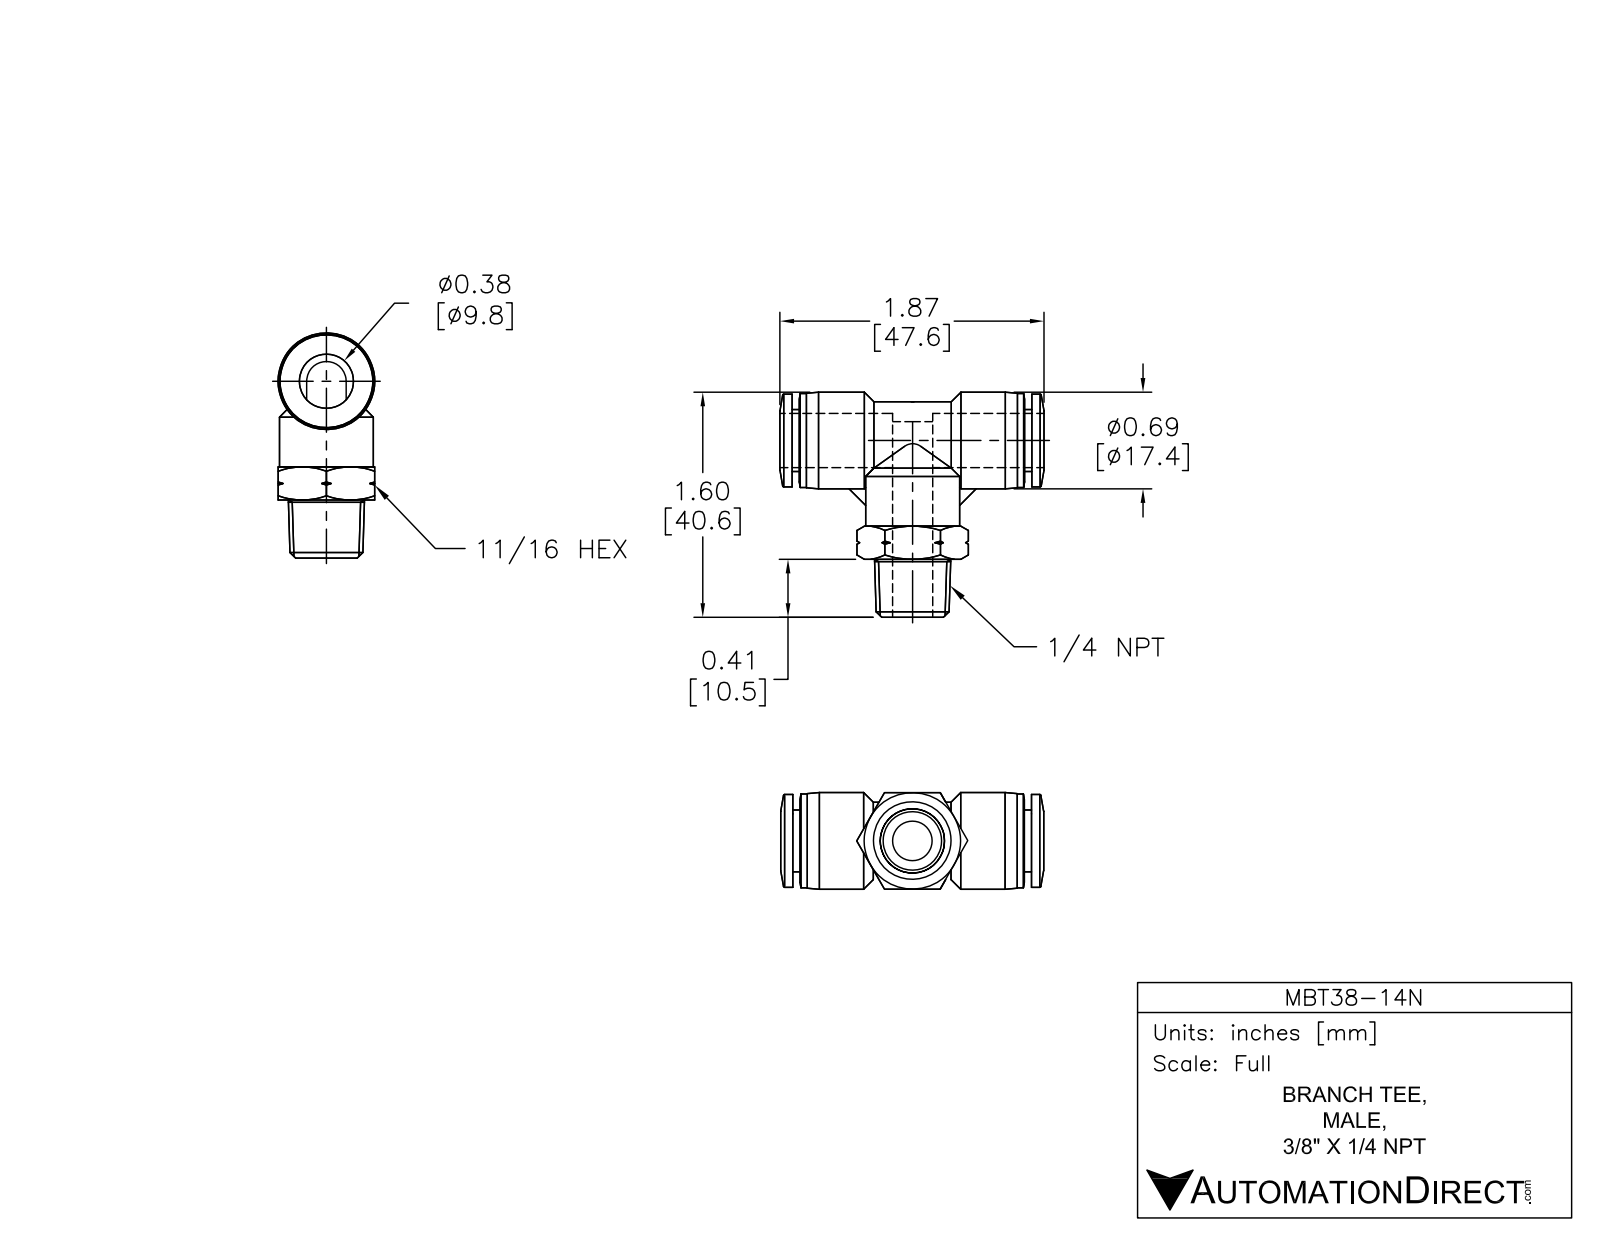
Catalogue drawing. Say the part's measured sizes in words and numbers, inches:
The part is named "MBT38-14N". Its 3-D file was written by "SolidWorks 2015 (AUTOMOTIVE_DESIGN)". It is 1 solid with 112 faces: 23 planar, 31 cylindrical and 58 other. Overall it measures 1.874 by 1.604 by 0.689 inches. Its volume is 0.632 cubic inches and its surface area 10.22 square inches. Round holes: 2 of diameter 0.276, 1 of diameter 0.386. Round bosses or shafts: 2 of diameter 0.669, 1 of diameter 0.689, 1 of diameter 0.661, 1 of diameter 0.441. Partial cylindrical surfaces (rounded edges, fillets, slot ends): 2 of radius 0.276. The main face-to-face distances are 0.687, 0.051, 1.65, 1.701, 1.598, 0.705, 0.996, 0.654, 0.945, 0.413.
